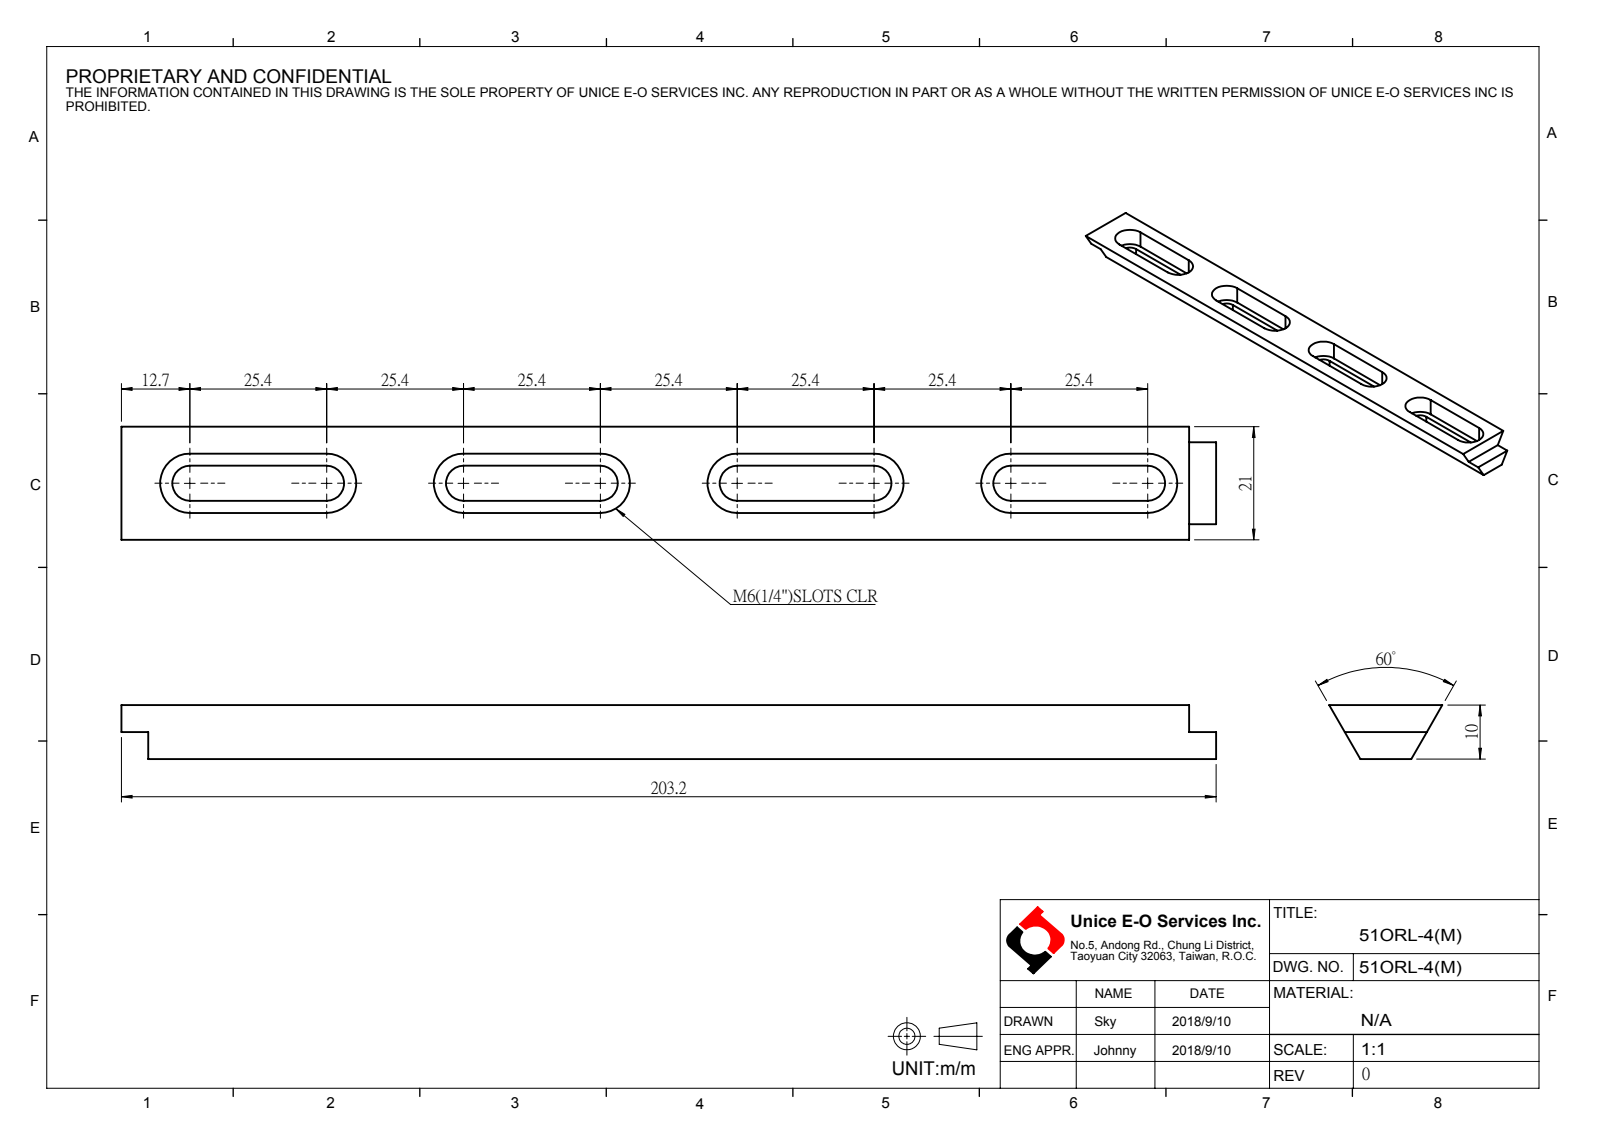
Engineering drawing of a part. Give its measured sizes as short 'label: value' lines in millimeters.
name: 51ORL-4(M)
written by: SolidWorks 2016 (AUTOMOTIVE_DESIGN)
unit: mm
bodies: 0 solids, 46 faces (30 planar, 16 cylindrical, 0 other)
size: 203.2 × 21 × 10
rounds: 8× R3.25, 8× R5.5
face distances: 10, 6.5, 2.25, 8.75, 3.5, 11, 5, 198.2, 1.5, 203.2
